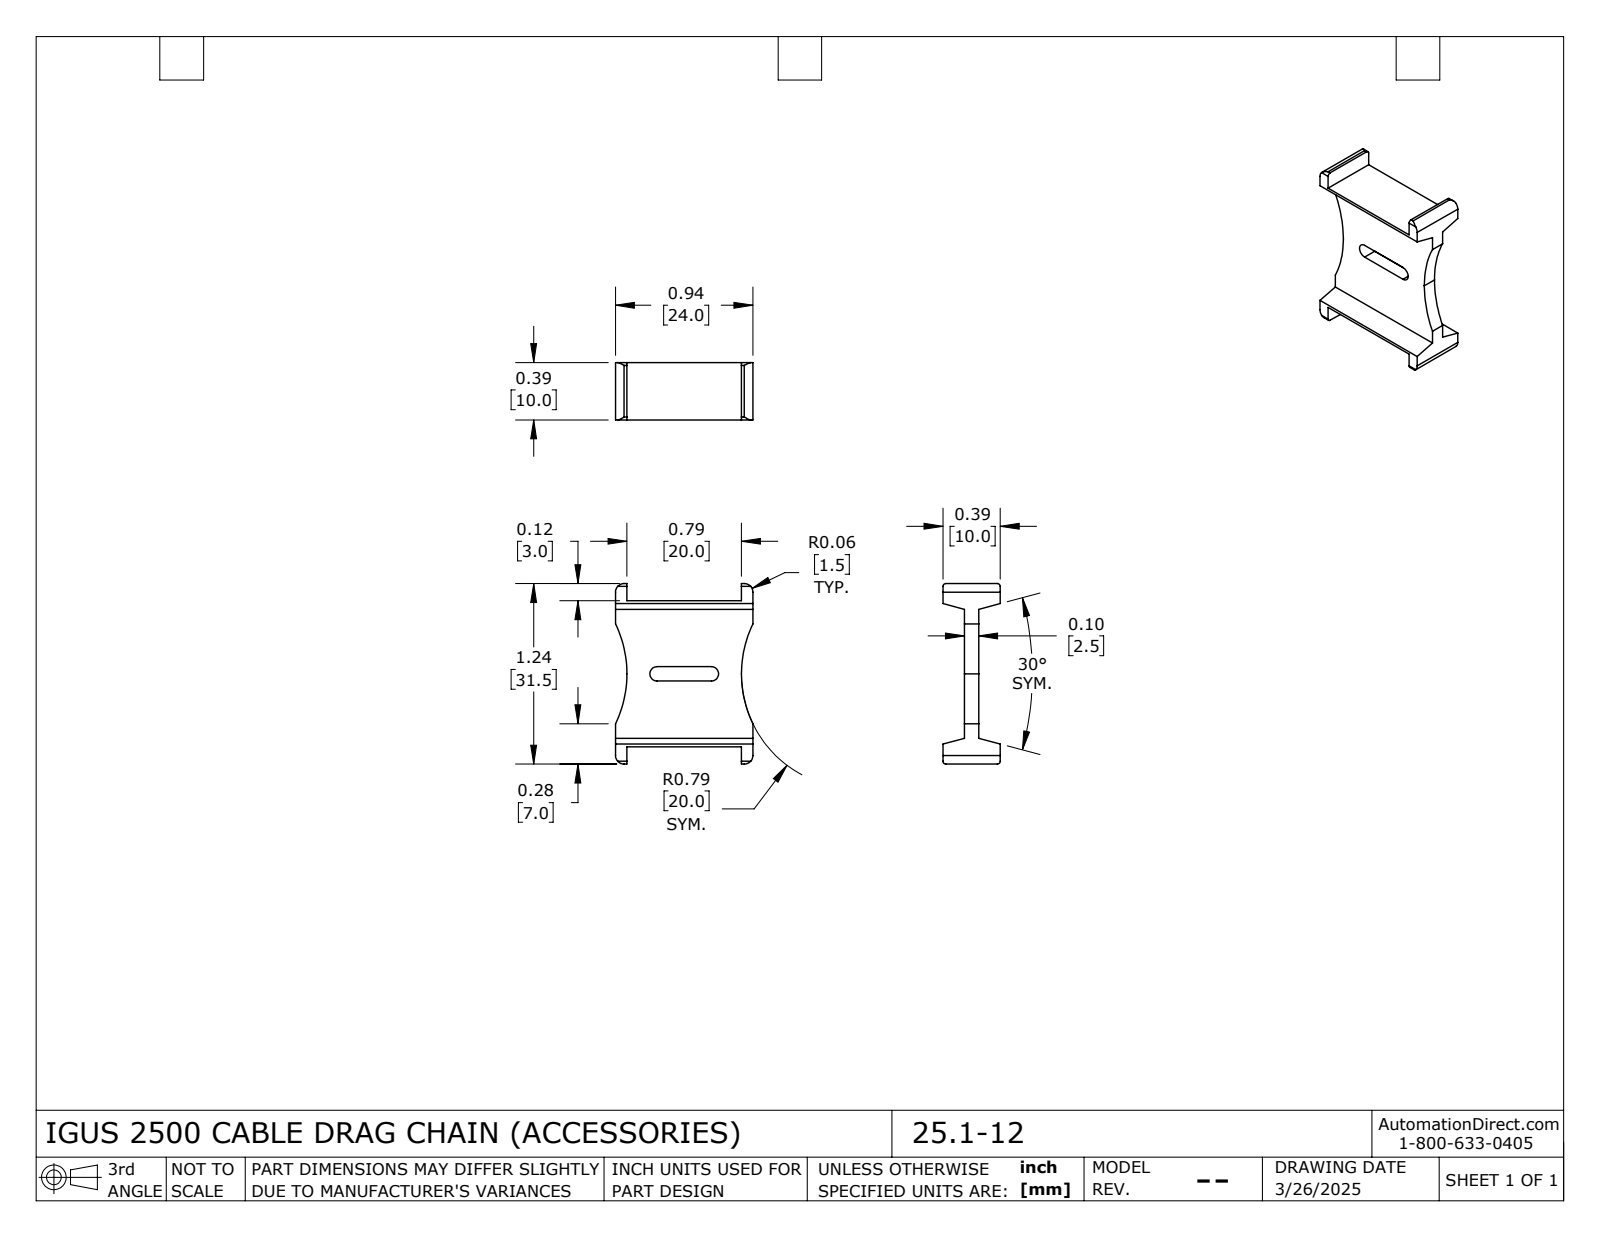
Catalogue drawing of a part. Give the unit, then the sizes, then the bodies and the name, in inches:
Units: inches
Overall size (bounding box): 1.24 × 0.945 × 0.394
Partial cylindrical surfaces — rounded edges, fillets, slot ends (radius × count): R0.02 ×4, R0.059 ×4, R0.049 ×2, R0.787 ×2
Main face-to-face distances: 0.098, 1.004, 0.83, 0.079, 0.866, 0.148, 0.246, 0.945, 0.787, 0.453
Volume: 0.117 in³ · Surface area: 3.585 in²
Bodies: 1 solid, 44 faces (26 planar, 18 cylindrical, 0 other)
Part name (STEP PRODUCT): 25_1
STEP written by: SolidWorks 2024 (AUTOMOTIVE_DESIGN)
